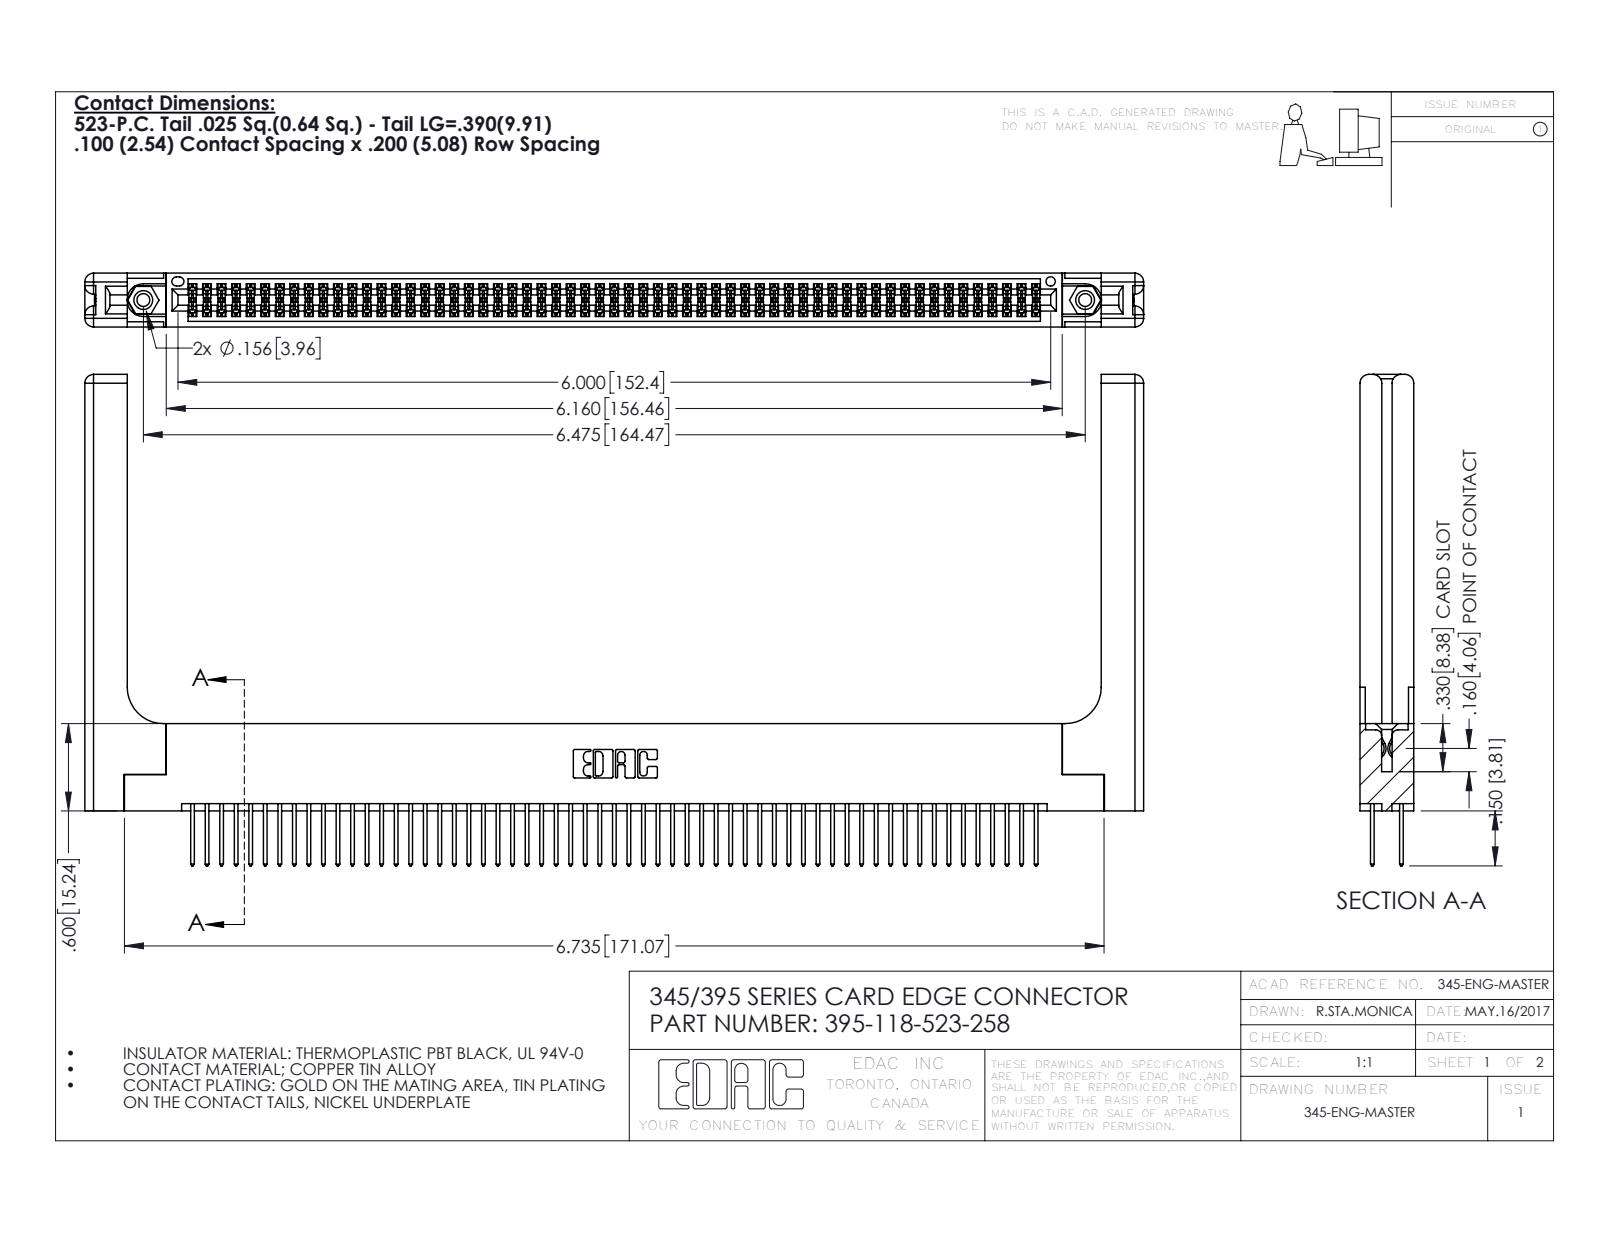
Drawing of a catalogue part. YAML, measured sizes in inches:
part_name: "345-220-058_345-220-058; 345-292-001_345-293-123; 345 Part_Flush Mounting Lugs - 0.156 Dia-TH; 345-250-001_345-250-001-102 (+1 more)"
step_written_by: "SolidWorks 2016 (CONFIG_CONTROL_DESIGN)"
units: inches
bodies: {solids: 123, faces: 6282, planar: 4122, cylindrical: 2100, other: 60}
overall_size: [7.279, 3.377, 0.37]
volume: 1.638
surface_area: 52.1
round_holes:
  - {diameter: 0.089, count: 2}
  - {diameter: 0.125, count: 2}
  - {diameter: 0.156, count: 2}
  - {diameter: 0.064, count: 1}
round_bosses_or_shafts:
  - {diameter: 0.155, count: 2}
partial_cylinders:
  - {radius: 0.006, count: 177}
  - {radius: 0.01, count: 118}
  - {radius: 0.01, count: 22}
  - {radius: 0.06, count: 16}
  - {radius: 0.007, count: 6}
  - {radius: 0.031, count: 6}
  - {radius: 0.026, count: 3}
  - {radius: 0.014, count: 2}
face_to_face_distances: [0.072, 0.298, 0.37, 0.2, 0.098, 0.272, 0.025, 0.225, 0.175, 0.148]
hole_center_spacings: [0.27, 6.239, 6.475]
